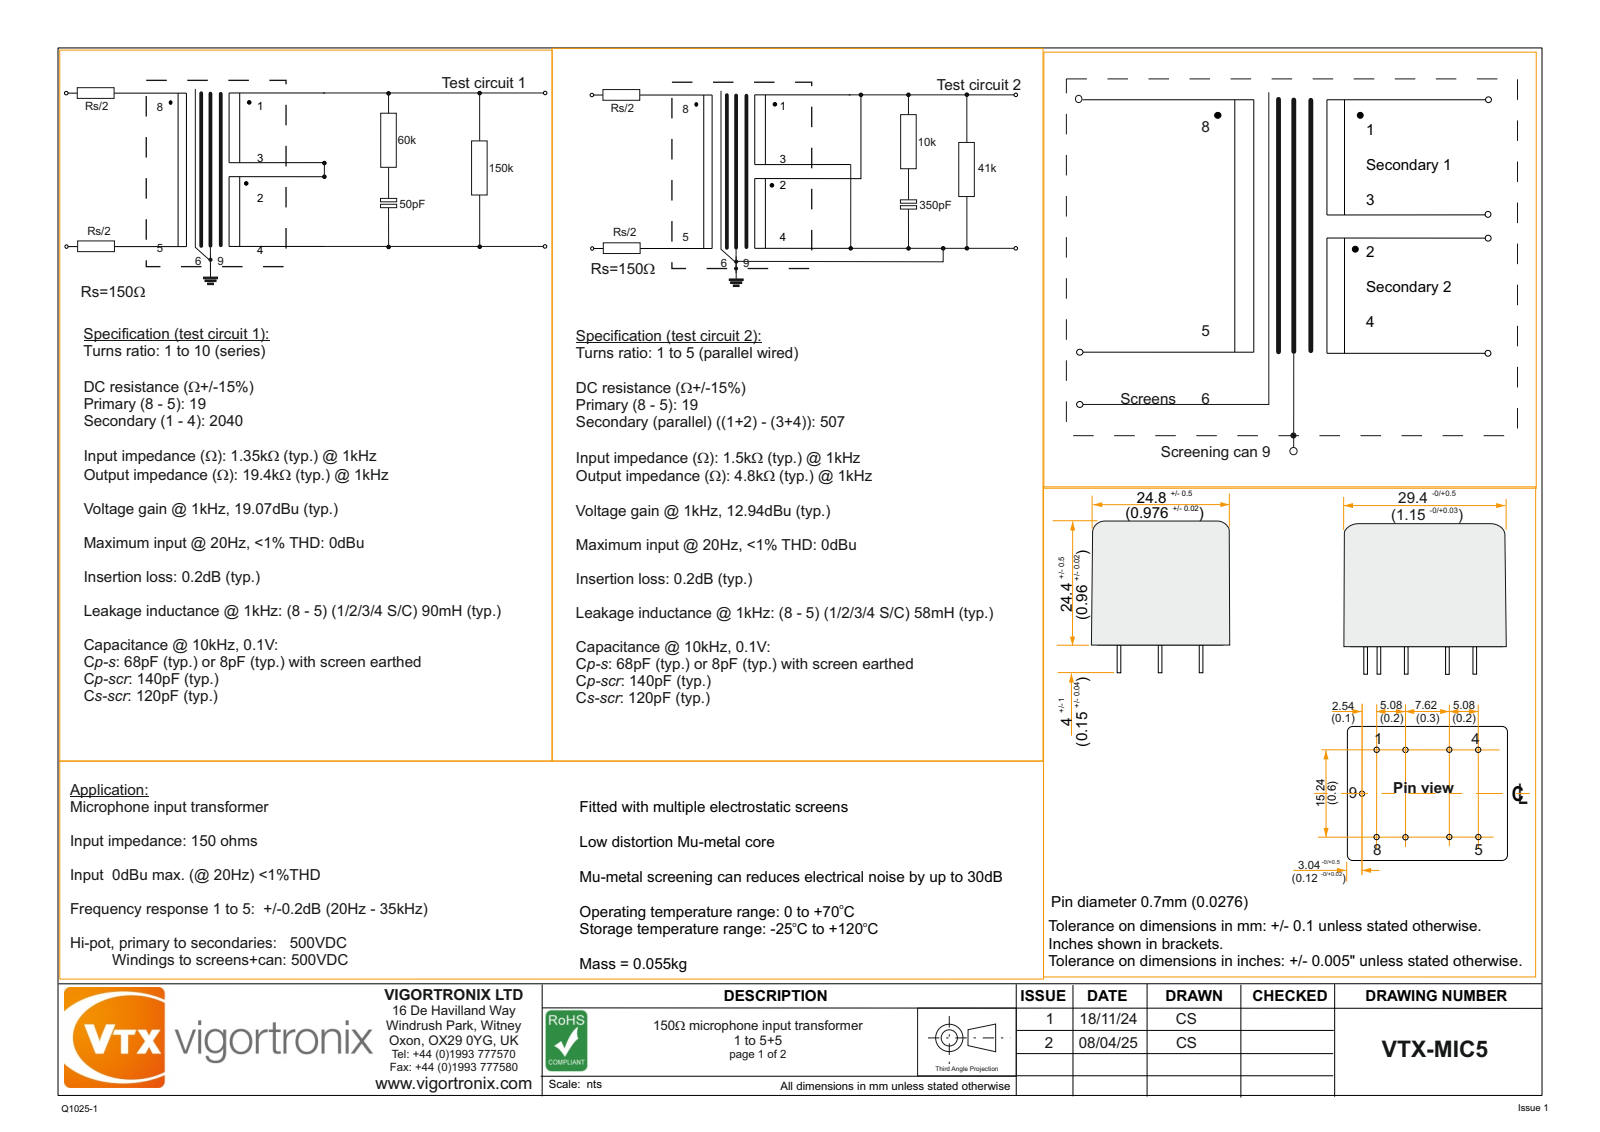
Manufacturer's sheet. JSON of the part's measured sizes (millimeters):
{"part_name": "VTX-MIC5; VTX-MIC5 LID; VTX-MIC5 BOBBIN; VTX-MIC5 CAN", "step_written_by": "SolidWorks 2024 (AUTOMOTIVE_DESIGN)", "units": "millimeters", "bodies": {"solids": 3, "faces": 130, "planar": 36, "cylindrical": 74, "other": 20}, "overall_size": [29.62, 28.6, 25.22], "volume_mm3": 15314, "surface_area_mm2": 10856, "round_holes": [[3.5, 8], [1.5, 1]], "round_bosses_or_shafts": [[0.7, 8]], "partial_cylinders_radius": [[0.5, 20], [1.9, 8], [2.5, 8], [2, 4]], "face_to_face_distances": [0.6, 23.4, 22.8, 22.5, 0.9, 23.1, 24, 23, 27.5, 2.6], "hole_center_spacings": [5.08, 12.7, 15.24, 16.06, 17.04, 19.84, 7.62, 8.03]}
